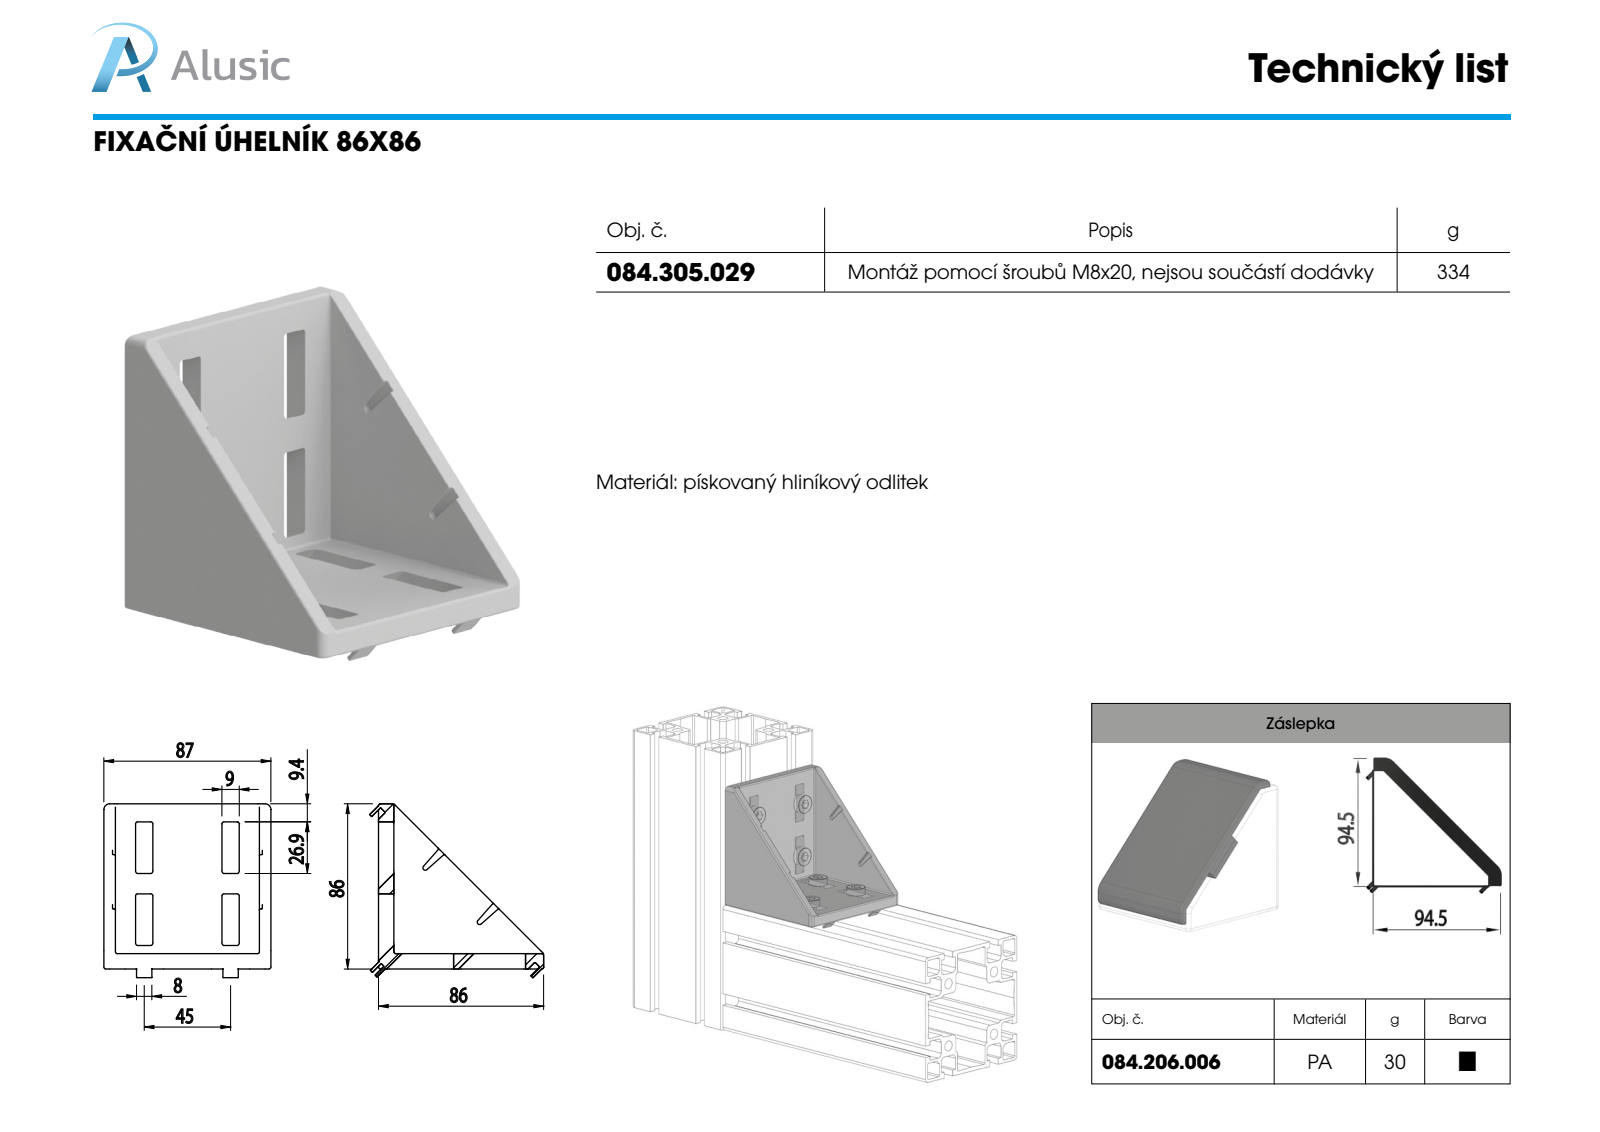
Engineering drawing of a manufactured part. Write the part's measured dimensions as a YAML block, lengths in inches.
part_name: "084.305.029"
step_written_by: "SolidWorks 2011 (CONFIG_CONTROL_DESIGN)"
units: inches
bodies: {solids: 1, faces: 687, planar: 152, cylindrical: 263, other: 272}
overall_size: [3.543, 3.543, 3.465]
volume: 7.691
surface_area: 78.59
partial_cylinders:
  - {radius: 0.039, count: 110}
  - {radius: 0.012, count: 60}
  - {radius: 0.02, count: 18}
  - {radius: 0.079, count: 3}
  - {radius: 0.046, count: 2}
face_to_face_distances: [0.197, 0.236, 0.394, 1.77, 3.386, 3.189, 2.992, 1.667, 0.667, 1]
